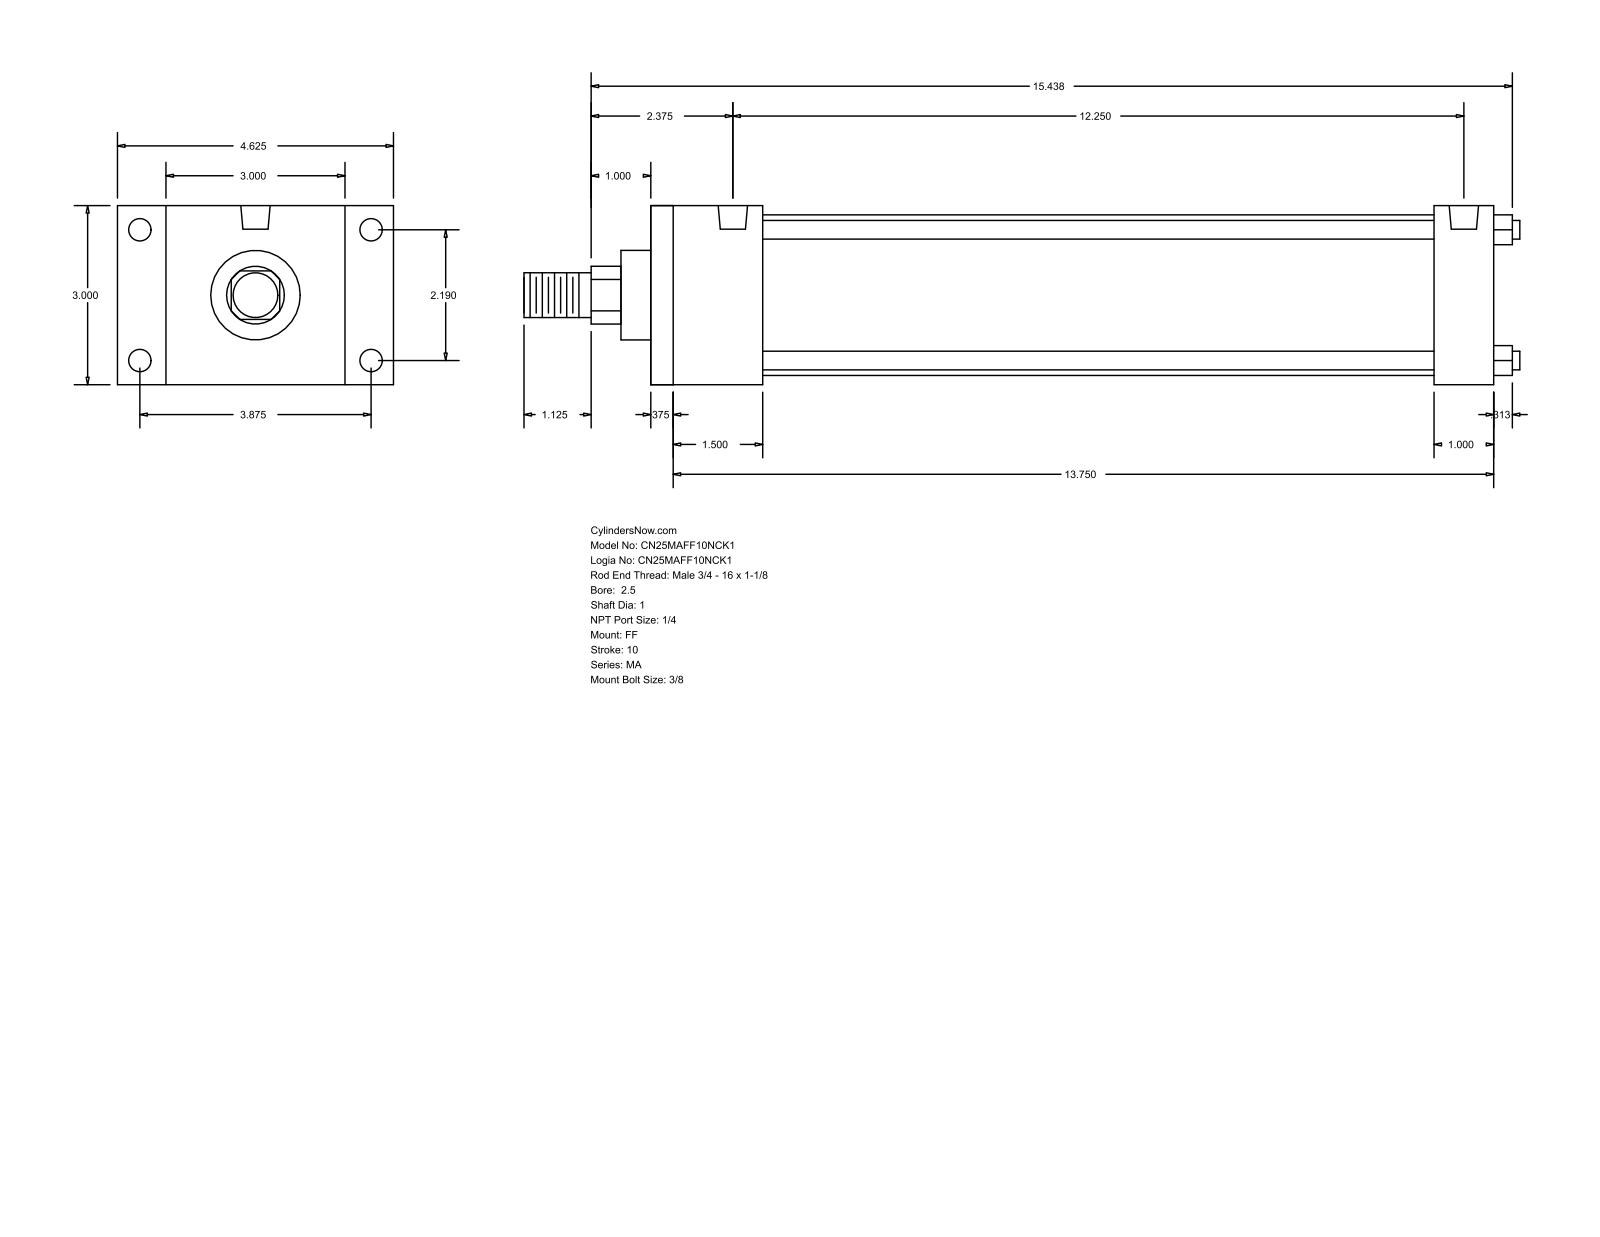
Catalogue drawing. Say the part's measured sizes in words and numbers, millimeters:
The part is named "MA_FF__0250_1". Its 3-D file was written by "GSSL Pune (CONFIG_CONTROL_DESIGN)". It is 0 solids with 92 faces: 64 planar, 28 cylindrical and 0 other. Overall it measures 423.86 by 117.47 by 76.2 millimeters. Round holes: 4 of diameter 7.94, 4 of diameter 9.53, 2 of diameter 12.49. Round bosses or shafts: 4 of diameter 7.94, 1 of diameter 68.33, 1 of diameter 38.1, 1 of diameter 25.4, 1 of diameter 19.05. Partial cylindrical surfaces (rounded edges, fillets, slot ends): 1 of radius 12.29. The main face-to-face distances are 76.2, 358.78, 9.52, 349.26, 47.63, 333.37, 38.11, 323.85, 285.74, 311.15. The hole center spacings are 55.62, 98.42, 113.05, 311.15.
